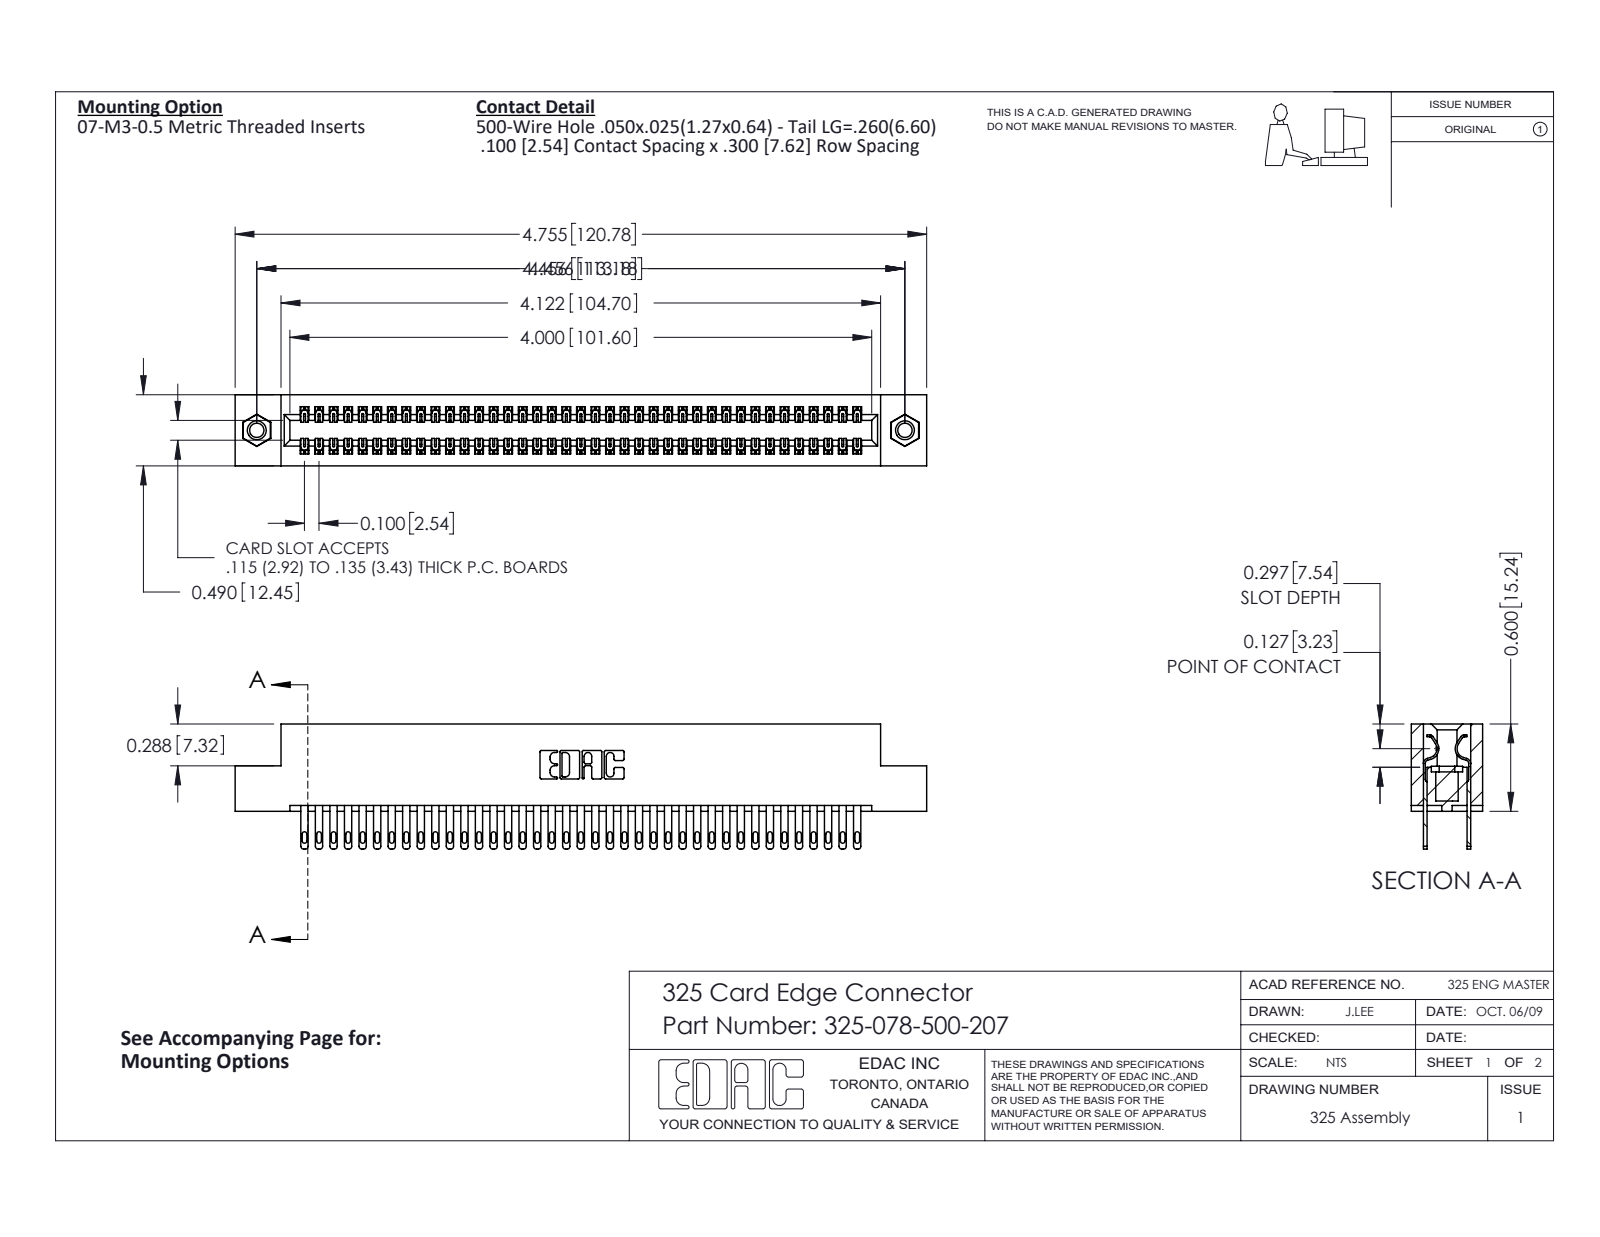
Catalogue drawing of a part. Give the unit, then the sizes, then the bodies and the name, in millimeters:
Units: millimetres
Overall size (bounding box): 120.8 × 21.8 × 12.4
Round holes (diameter × count): ⌀2.5 ×2, ⌀3.2 ×2, ⌀4.1 ×2
Round bosses / shafts (diameter × count): ⌀3.9 ×2
Partial cylindrical surfaces — rounded edges, fillets, slot ends (radius × count): R0.2 ×117, R0.4 ×78, R0.5 ×78, R0.3 ×22, R0.2 ×6, R0.8 ×6, R0.7 ×3, R0.4 ×2
Main face-to-face distances: 2.1, 10.3, 7.6, 2.7, 9.7, 0.6, 12.4, 8.3, 7, 14.2
Hole centre spacings: 113.2
Volume: 15 800 mm³ · Surface area: 19 880 mm²
Bodies: 81 solids, 3918 faces (2442 planar, 1460 cylindrical, 16 other)
Part name (STEP PRODUCT): 325-078-500-207; 345-250-001_345-250-005-103; 325 Part_TI; 325-292-001_325-293-100
STEP written by: SolidWorks 2016 (CONFIG_CONTROL_DESIGN)
